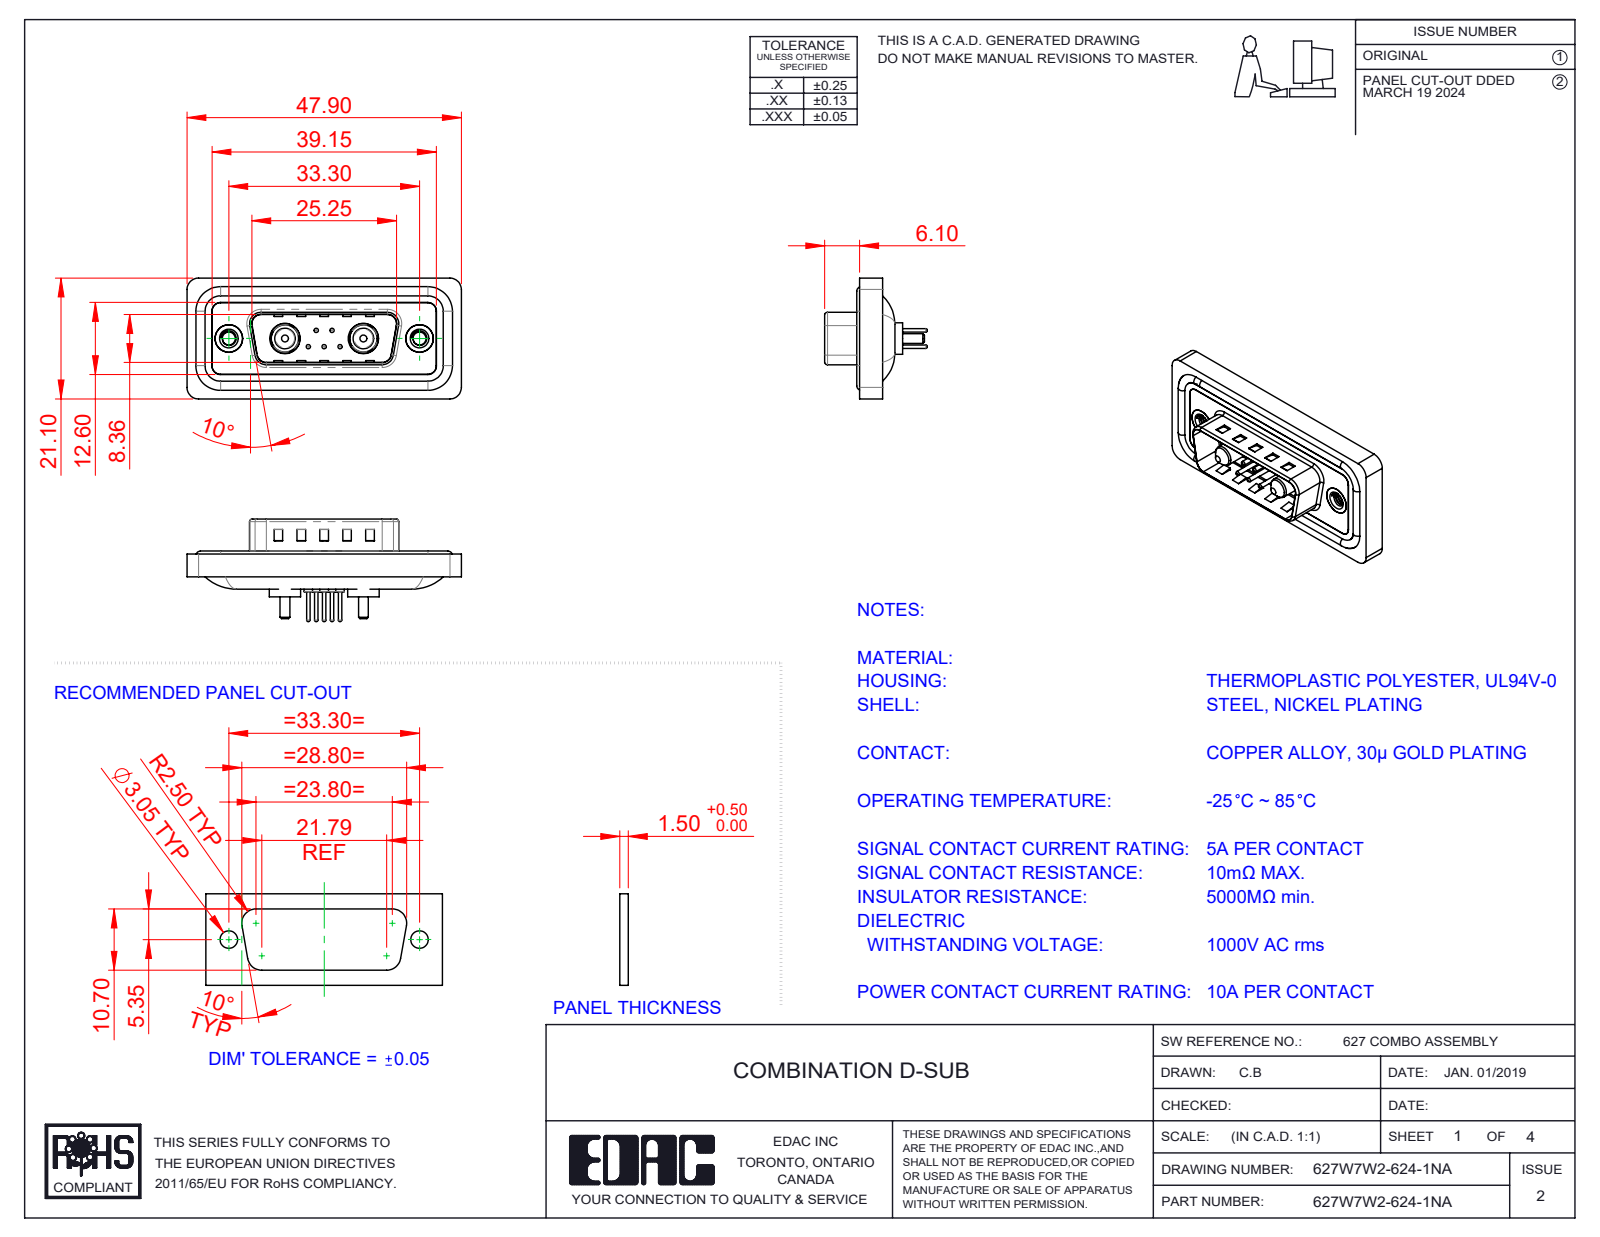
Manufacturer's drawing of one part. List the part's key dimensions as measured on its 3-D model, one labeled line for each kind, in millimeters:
Part name (STEP PRODUCT): 627Combo Shell Front_15 Contacts; 627Combo Shell Rear_15 Contacts; 627Combo Housing_7W2; Power Pin_10A S (+5 more)
STEP written by: SolidWorks 2023 (CONFIG_CONTROL_DESIGN)
Units: millimetres
Bodies: 16 solids, 708 faces (232 planar, 294 cylindrical, 182 other)
Overall size (bounding box): 47.9 × 21.1 × 17.9
Volume: 5 489 mm³ · Surface area: 8 765 mm²
Round holes (diameter × count): ⌀0.75 ×5, ⌀1.6 ×5, ⌀2 ×5, ⌀2.26 ×2, ⌀4 ×2, ⌀4.8 ×2, ⌀4.85 ×2, ⌀5 ×2, ⌀5.3 ×2
Round bosses / shafts (diameter × count): ⌀1.5 ×5, ⌀0.6 ×5, ⌀1.6 ×4, ⌀5.5 ×2, ⌀5.2 ×2, ⌀4.9 ×2, ⌀4.75 ×2, ⌀3.75 ×2
Partial cylindrical surfaces — rounded edges, fillets, slot ends (radius × count): R1.5 ×26, R2 ×20, R0.5 ×8, R1.6 ×8, R0.25 ×4, R0.6 ×4, R0.65 ×4, R0.9 ×4
Main face-to-face distances: 0.4, 1.1, 1.5, 1.6, 0.5, 3.1, 2.9, 4, 0.82, 9.58
Hole centre spacings: 3.16, 2.77, 9.8, 23.5, 4.31, 4.33, 5.03, 5.04
